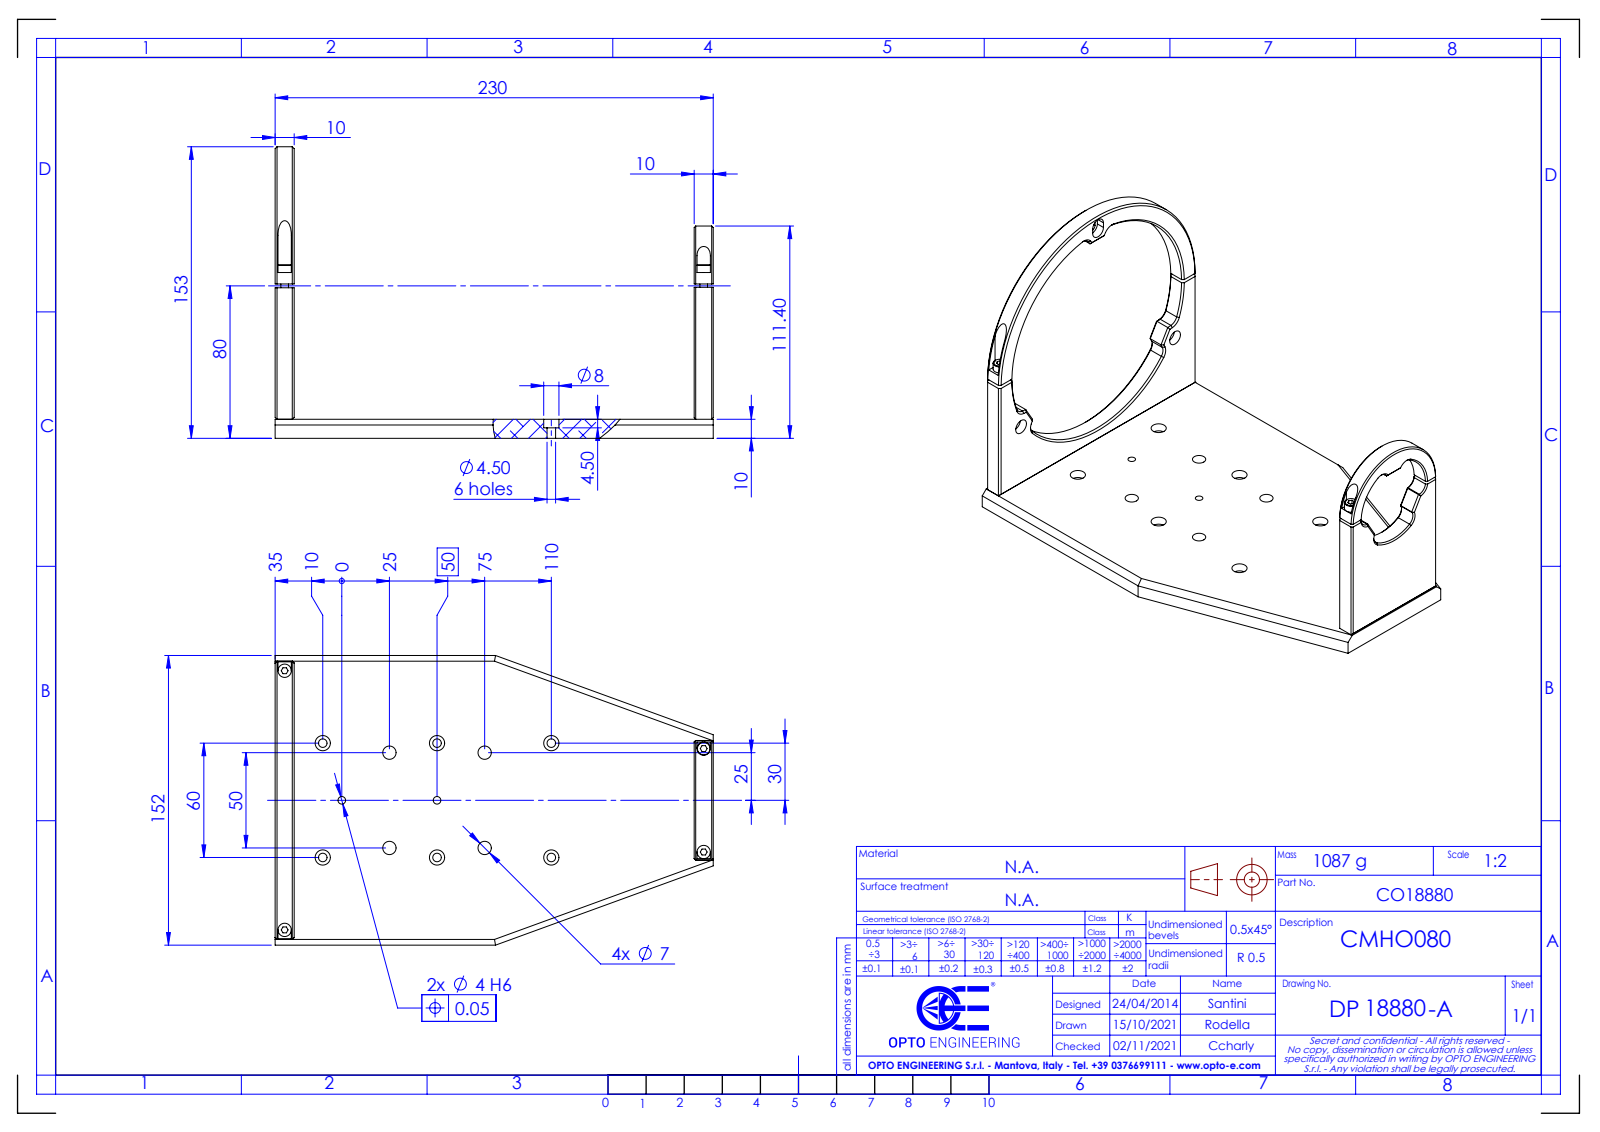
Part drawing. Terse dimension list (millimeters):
name: DP18880_CMHO080
written by: SolidWorks 2021 (CONFIG_CONTROL_DESIGN)
unit: mm
bodies: 0 solids, 321 faces (159 planar, 98 cylindrical, 64 other)
size: 230 × 153 × 152
holes: 12× ⌀8, 8× ⌀4.5, 6× ⌀7, 2× ⌀4, 1× ⌀126
bosses: 2× ⌀7, 2× ⌀4
rounds: 12× R5, 2× R2.25, 2× R4, 1× R23.9, 1× R31.4, 1× R73
face distances: 10, 220, 230, 210, 3, 44.6, 107.4, 149, 41.6, 104.4
hole spacings: 35.36, 60, 50, 25.5, 60.42, 65.19, 67.08, 84.85
